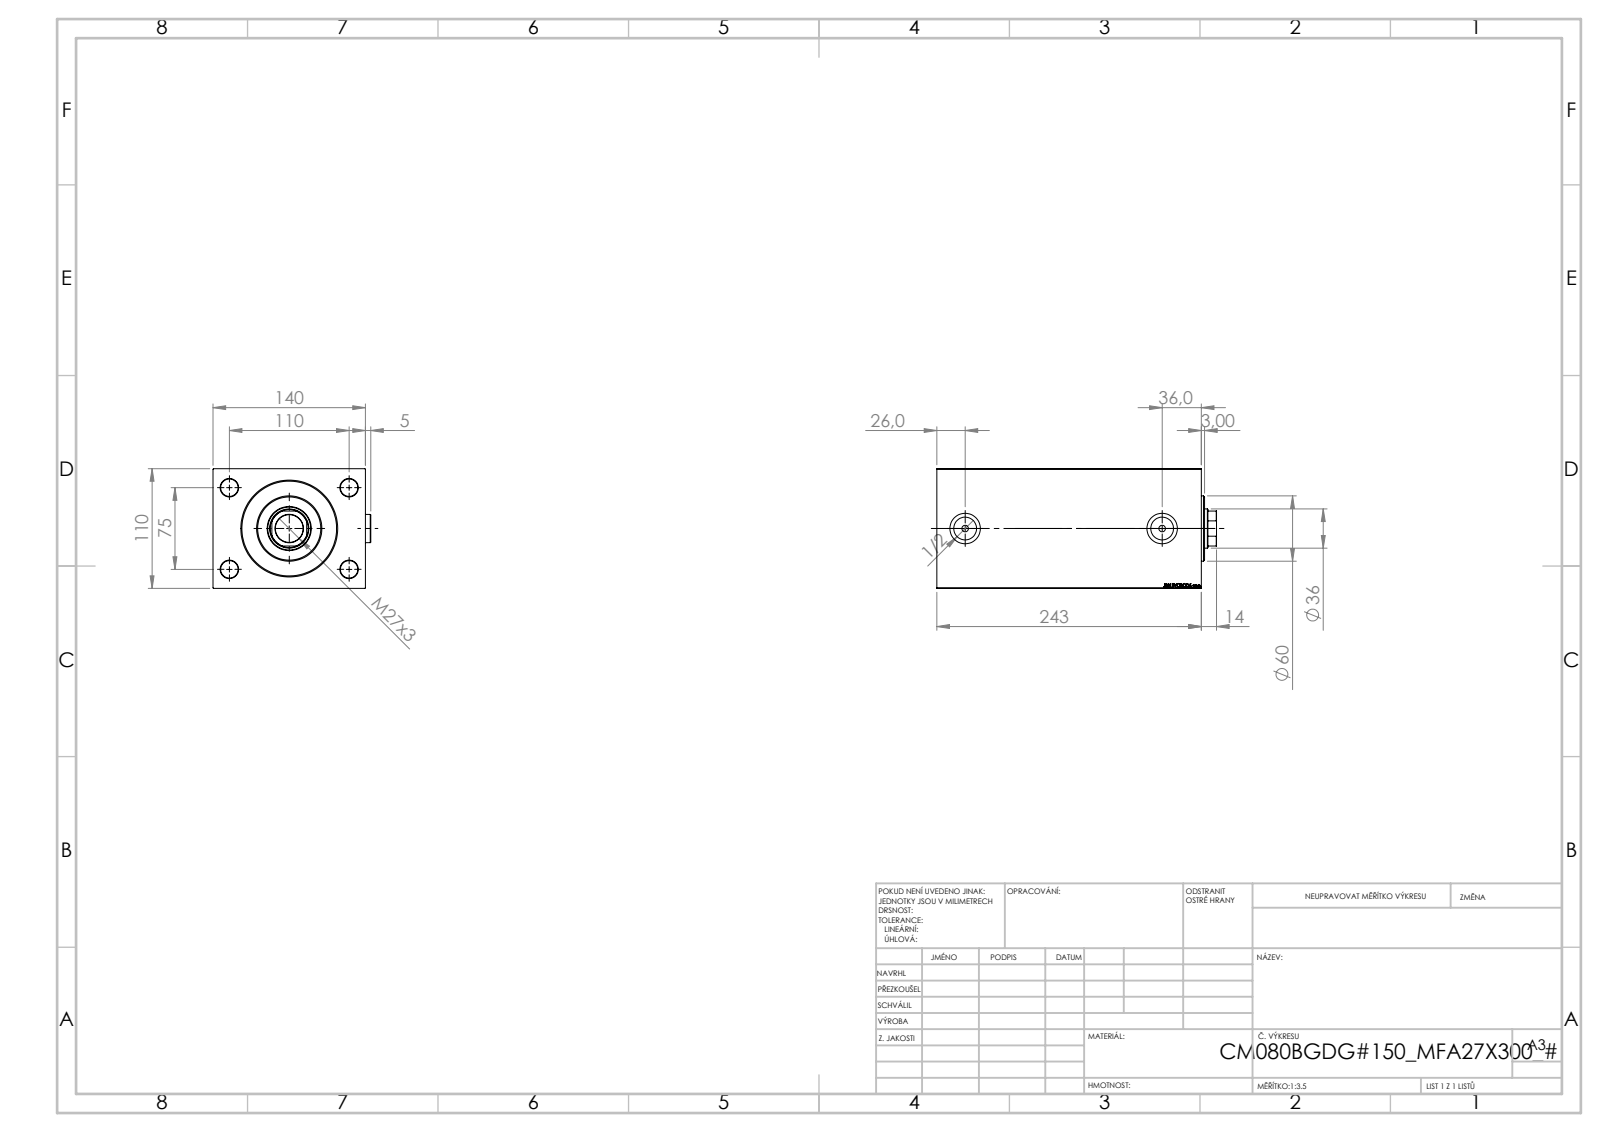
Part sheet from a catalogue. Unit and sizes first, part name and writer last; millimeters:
Units: millimetres
Overall size (bounding box): 257 × 144.9 × 110
Round holes (diameter × count): ⌀16 ×4, ⌀6 ×2, ⌀20.96 ×2, ⌀28 ×2, ⌀25.5 ×1, ⌀36 ×1, ⌀39.5 ×1, ⌀40.5 ×1, ⌀80 ×1, ⌀82 ×1, ⌀87 ×1
Round bosses / shafts (diameter × count): ⌀26 ×2, ⌀60 ×1
Partial cylindrical surfaces — rounded edges, fillets, slot ends (radius × count): R17.5 ×1
Main face-to-face distances: 110, 140, 243, 222, 21, 14, 208, 229, 164, 150
Hole centre spacings: 66.57, 75, 110, 133.14, 181
Volume: 3 075 000 mm³ · Surface area: 291 004 mm²
Bodies: 5 solids, 938 faces (436 planar, 72 cylindrical, 430 other)
Part name (STEP PRODUCT): V450CM_B_VCP; Zatka_OIL_PORT; V450CM_B_Body; V450CM_VC_B
STEP written by: SolidWorks 2019 (CONFIG_CONTROL_DESIGN)
